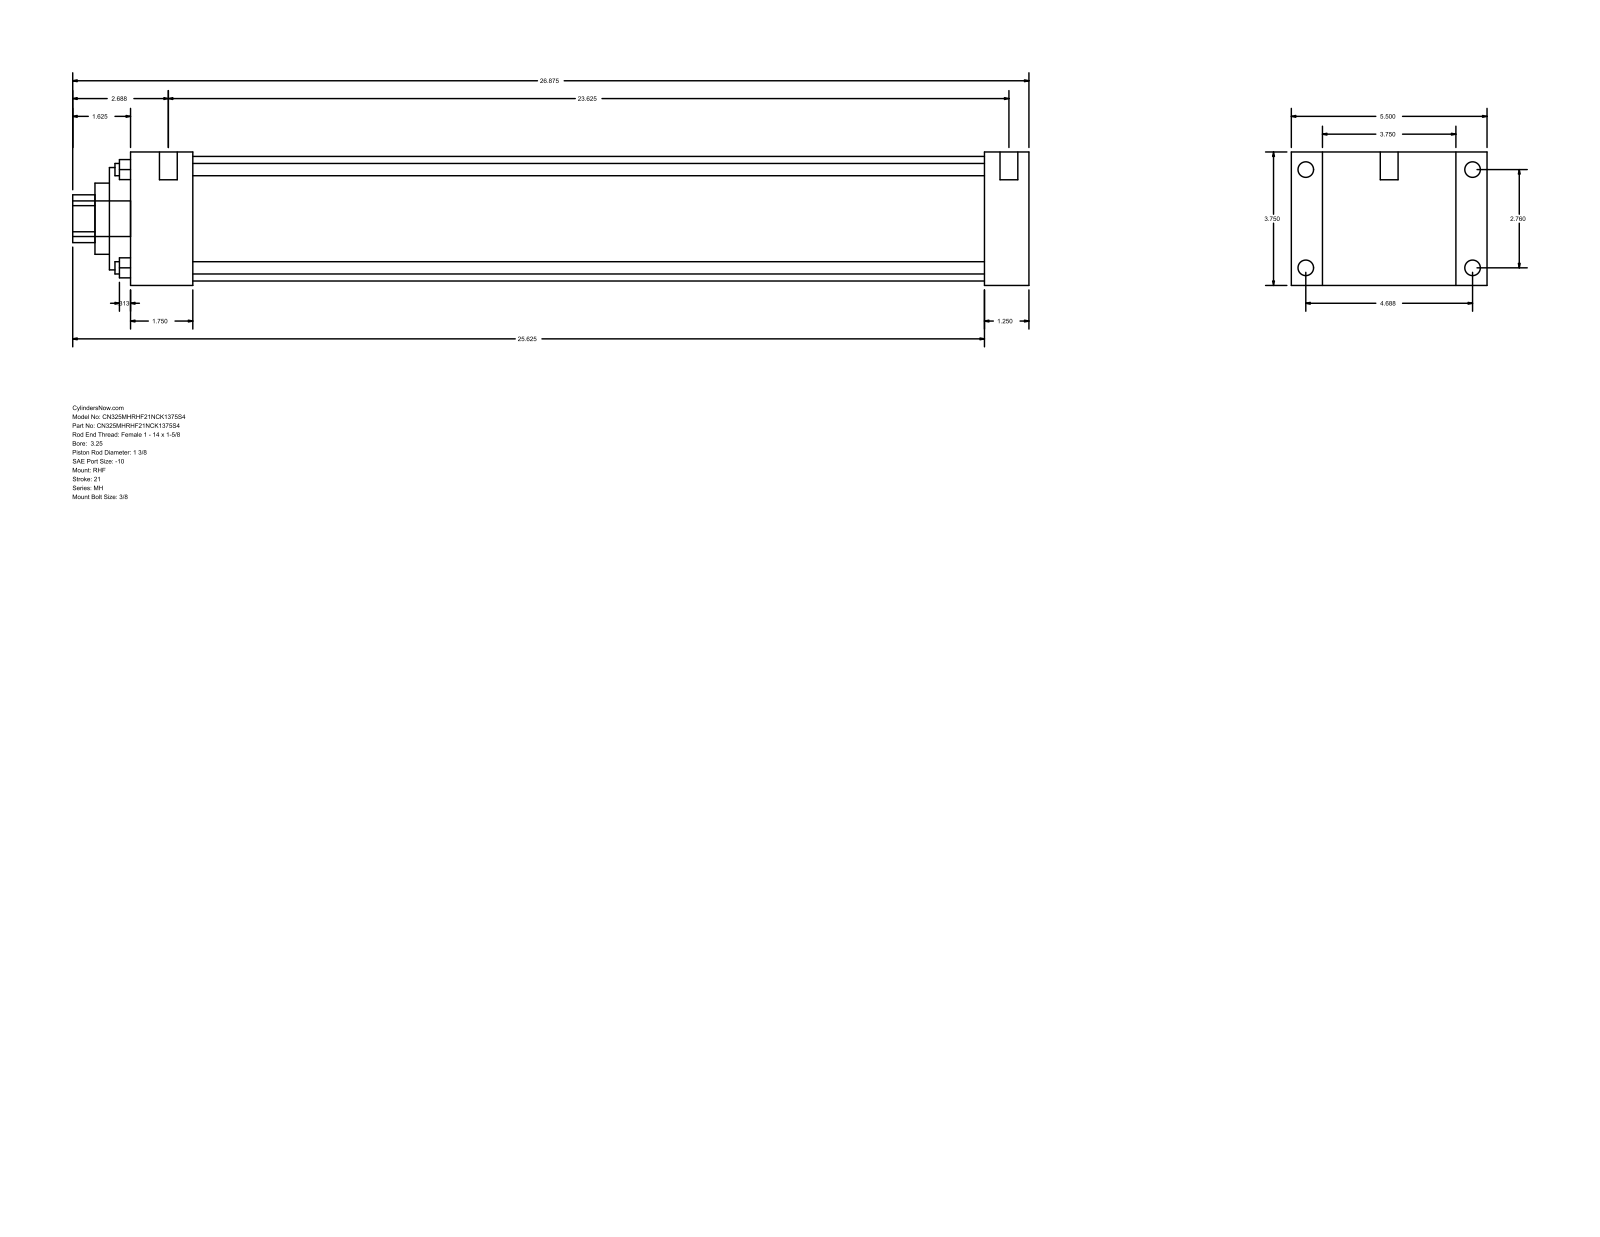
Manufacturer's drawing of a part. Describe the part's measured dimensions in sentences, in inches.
The part is named "MH_RHF__0325_1.375". Its 3-D file was written by "GSSL Pune (CONFIG_CONTROL_DESIGN)". It is 0 solids with 90 faces: 61 planar, 29 cylindrical and 0 other. Overall it measures 26.875 by 5.5 by 3.75 inches. Round holes: 4 of diameter 0.345, 1 of diameter 1.375, 1 of diameter 2, 1 of diameter 2.875, 1 of diameter 3.5. Round bosses or shafts: 4 of diameter 0.438, 4 of diameter 0.219, 2 of diameter 0.5, 1 of diameter 1. Partial cylindrical surfaces (rounded edges, fillets, slot ends): 1 of radius 0.672. The main face-to-face distances are 3.75, 1.25, 0.875, 4.625, 24, 25.25, 5.5, 1.75, 22.25, 23.5. The hole center spacings are 1.952, 2.76, 3.903.
